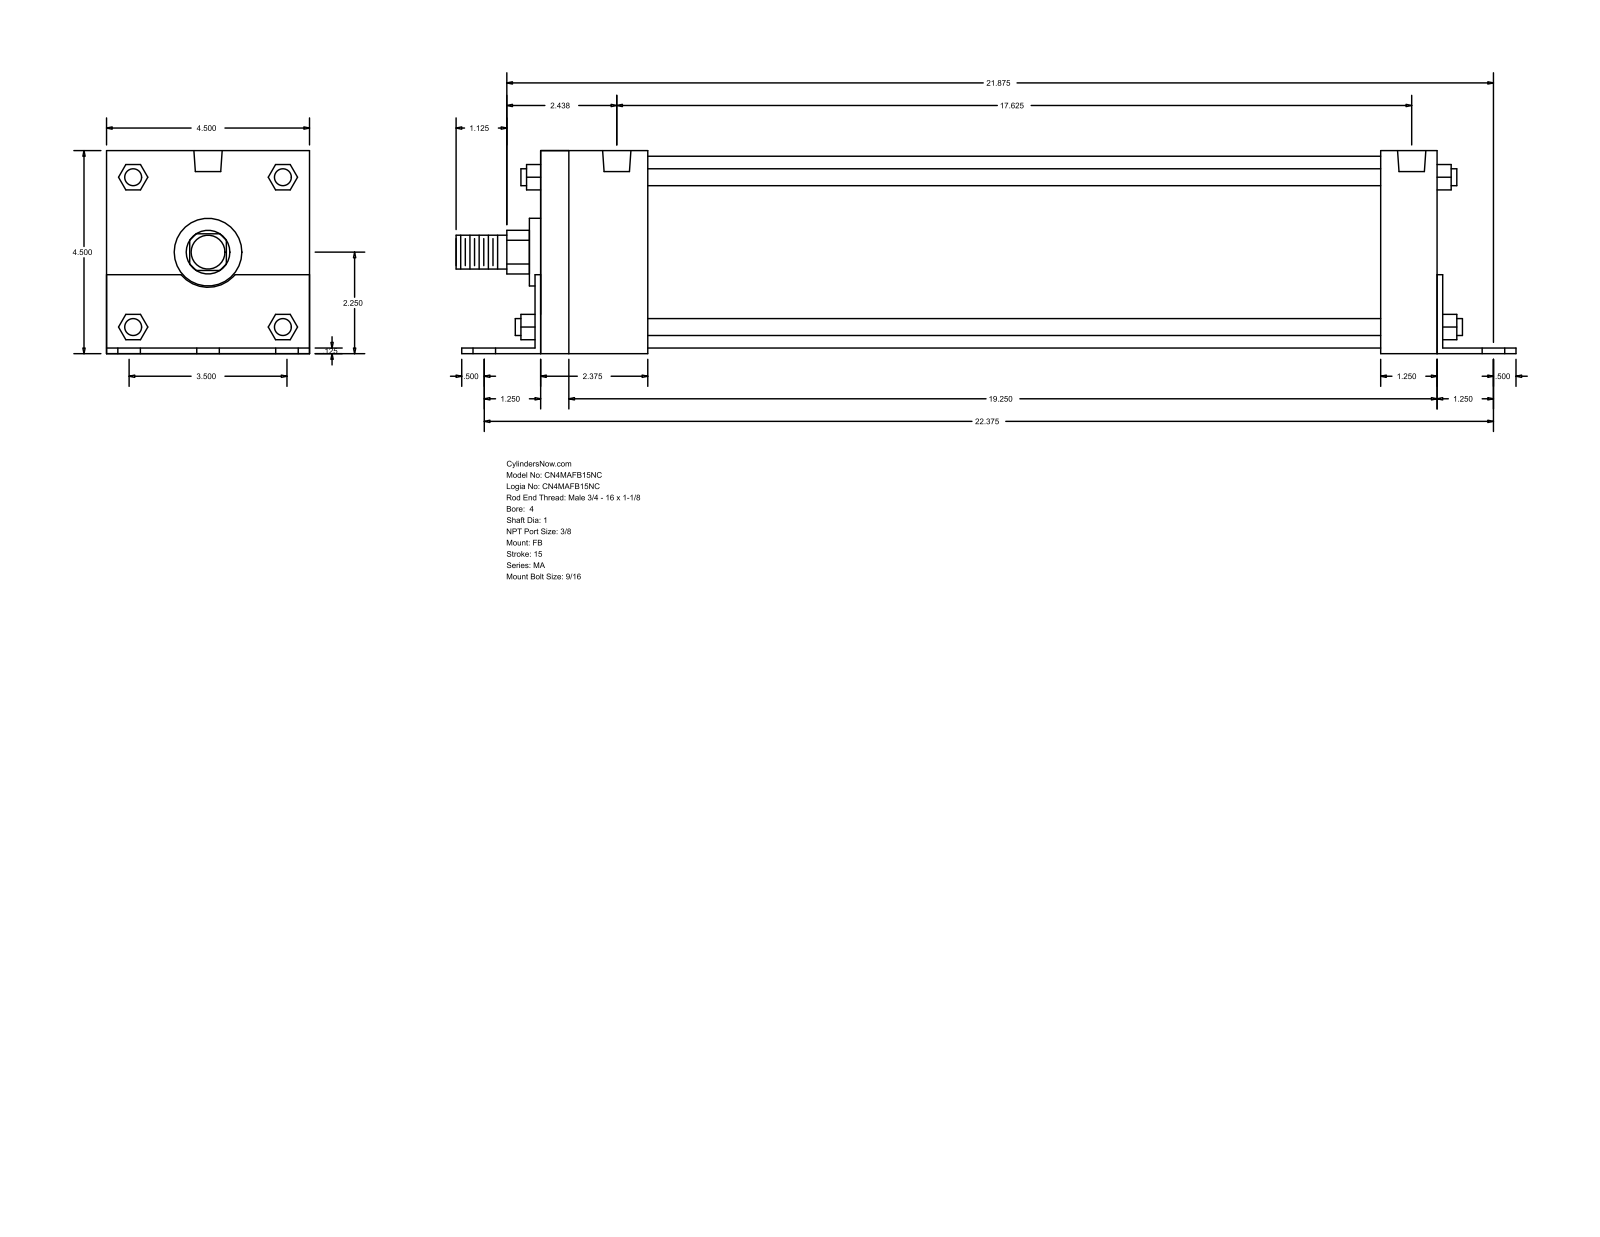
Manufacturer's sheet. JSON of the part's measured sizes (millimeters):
{"part_name": "MA_FB__0400_1", "step_written_by": "GSSL Pune (CONFIG_CONTROL_DESIGN)", "units": "millimeters", "bodies": {"solids": 0, "faces": 140, "planar": 105, "cylindrical": 35, "other": 0}, "overall_size": [596.9, 114.35, 114.3], "round_holes": [[14.29, 6], [11.11, 4], [15.93, 2]], "round_bosses_or_shafts": [[9.53, 4], [107.95, 1], [38.1, 1], [25.4, 1], [19.05, 1]], "partial_cylinders_radius": [[12.29, 1], [19.81, 1]], "face_to_face_distances": [114.3, 3.17, 114.35, 508, 3.12, 111.18, 504.83, 511.17, 34.93, 476.24], "hole_center_spacings": [44.45, 570.06, 568.32, 63.99, 67.5, 86.85, 88.9, 90.97]}
